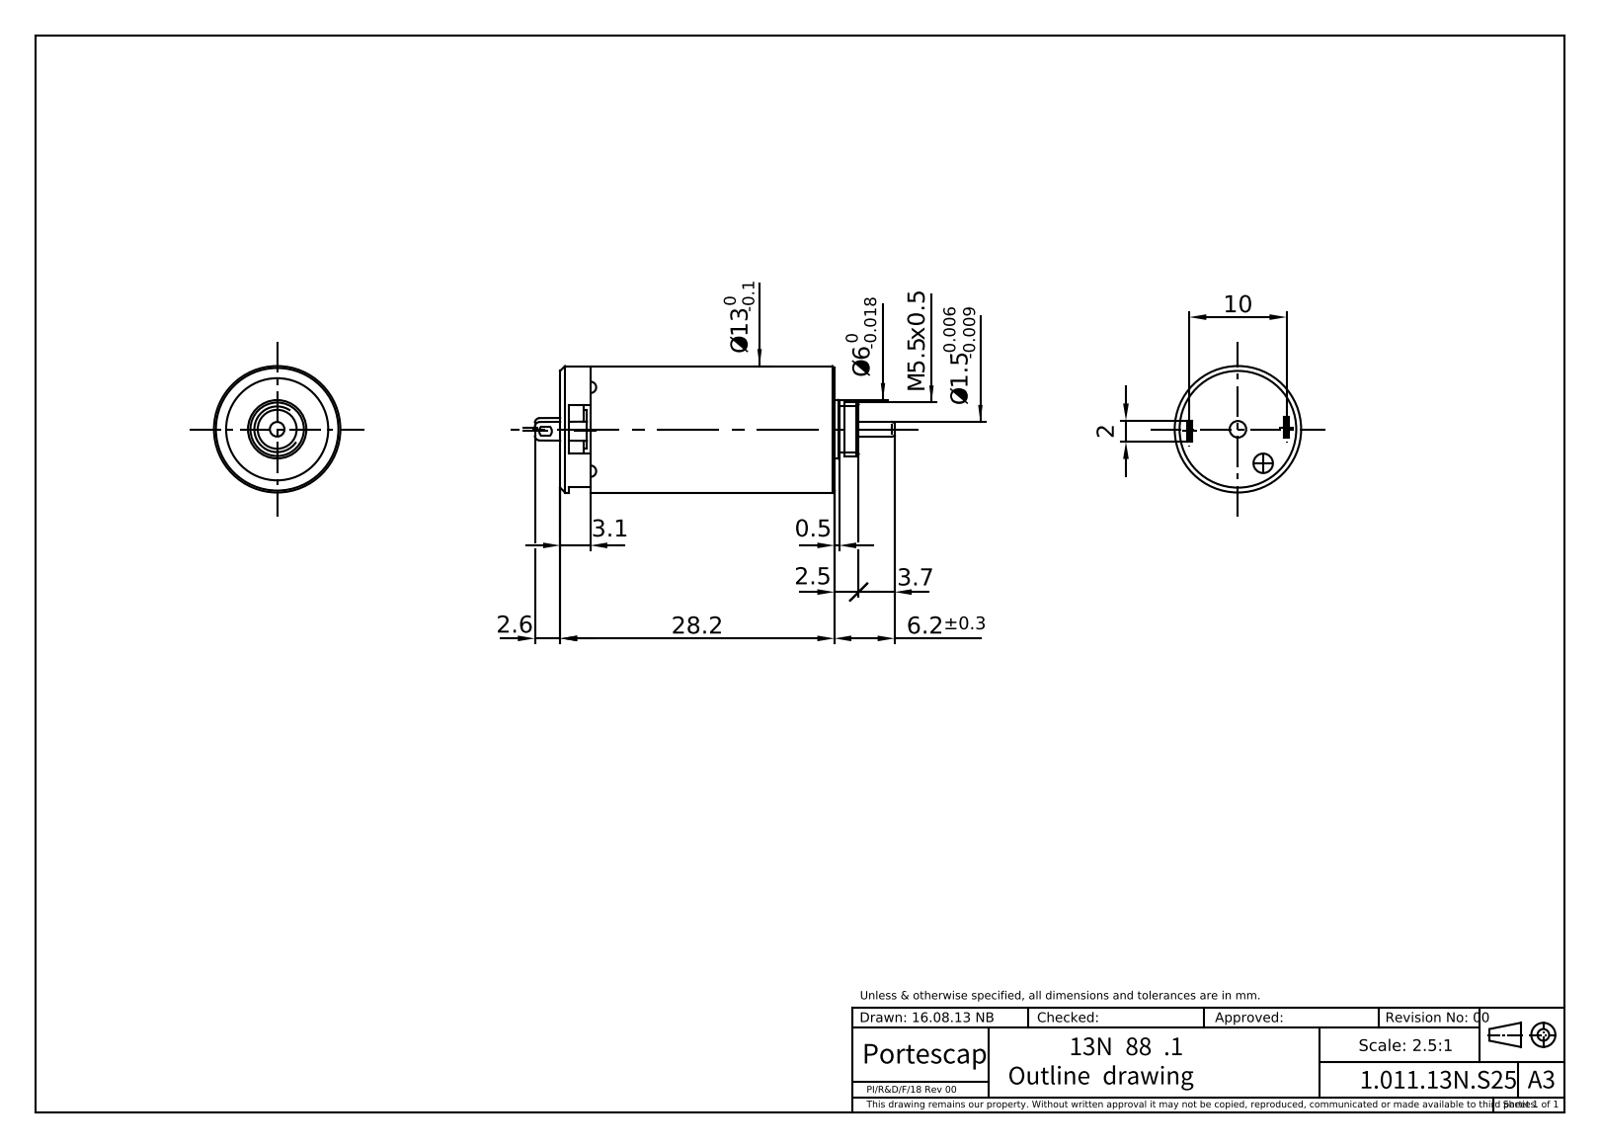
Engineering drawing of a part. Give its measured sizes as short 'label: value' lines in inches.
name: 13N_88_107__1
written by: PRO/ENGINEER BY PARAMETRIC TECHNOLOGY CORPORATION, 2014310 (CONFIG_CONTROL_DESIGN)
unit: in
bodies: 1 solid, 196 faces (83 planar, 84 cylindrical, 29 other)
size: 1.457 × 0.512 × 0.512
volume: 0.221 in³; area: 2.945 in²
holes: 1× ⌀0.065, 1× ⌀0.079, 1× ⌀0.413, 1× ⌀0.471, 1× ⌀0.488
bosses: 1× ⌀0.512, 1× ⌀0.511, 1× ⌀0.484, 1× ⌀0.236, 1× ⌀0.217, 1× ⌀0.197, 1× ⌀0.157, 1× ⌀0.059
rounds: 6× R0.037, 4× R0.006, 3× R0.079, 2× R0.02, 2× R0.038, 2× R0.039, 1× R0.03, 1× R0.039
face distances: 1.096, 0.014, 1.082, 0.091, 0.076, 1.006, 1.11, 1.096, 1.02, 0.014
hole spacings: 0.172
